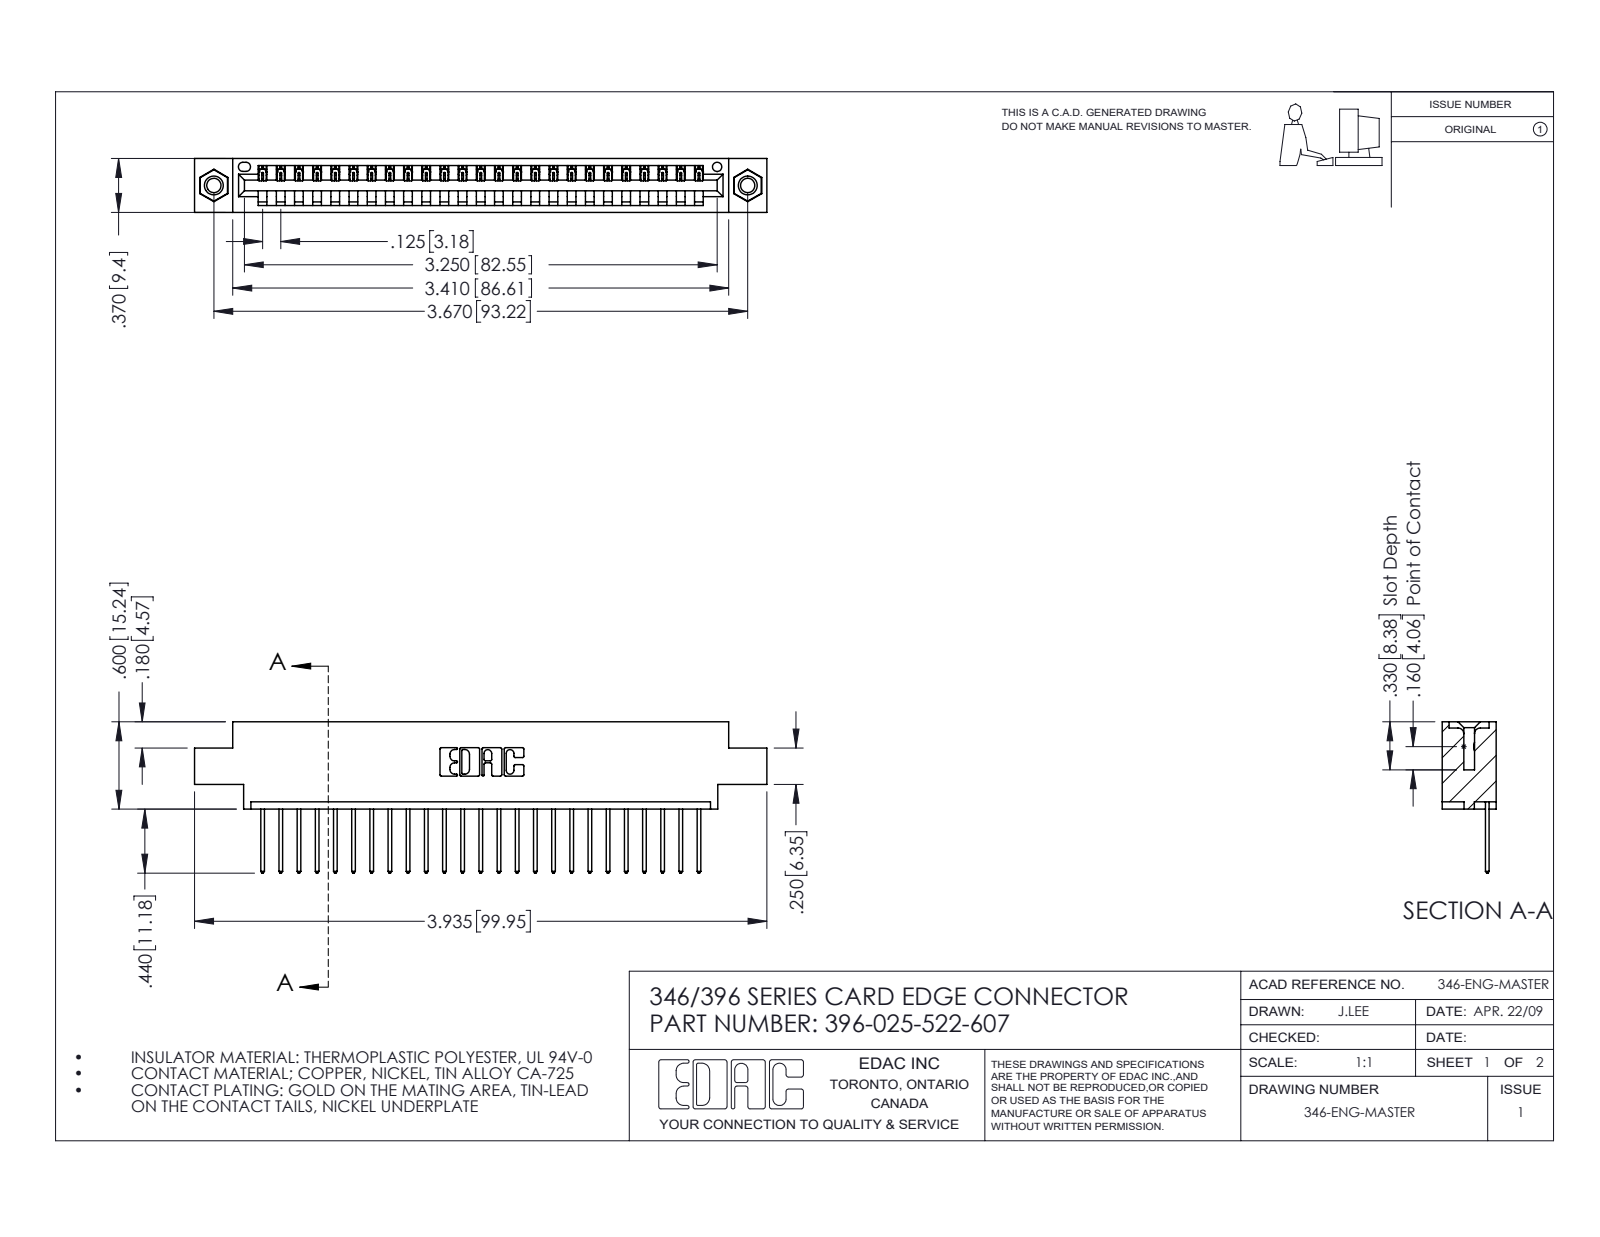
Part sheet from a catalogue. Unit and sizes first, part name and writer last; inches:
Units: inches
Overall size (bounding box): 3.935 × 1.04 × 0.37
Round holes (diameter × count): ⌀0.098 ×2, ⌀0.125 ×2, ⌀0.156 ×2, ⌀0.064 ×1
Round bosses / shafts (diameter × count): ⌀0.155 ×2
Partial cylindrical surfaces — rounded edges, fillets, slot ends (radius × count): R0.006 ×50, R0.01 ×50, R0.01 ×22, R0.007 ×6, R0.031 ×6, R0.026 ×3, R0.031 ×2, R0.04 ×2
Main face-to-face distances: 0.048, 0.322, 0.37, 0.25, 0.072, 0.298, 0.025, 0.222, 0.148, 0.1
Hole centre spacings: 0.246, 3.462, 3.67
Volume: 0.567 in³ · Surface area: 18.15 in²
Bodies: 28 solids, 1636 faces (1112 planar, 508 cylindrical, 16 other)
Part name (STEP PRODUCT): 346 Part_0.170 Offset - 0.156 Dia-TI; 345-250-001_345-250-005-103; 345-292-001_345-293-122; 396-025-522-607
STEP written by: SolidWorks 2016 (CONFIG_CONTROL_DESIGN)
